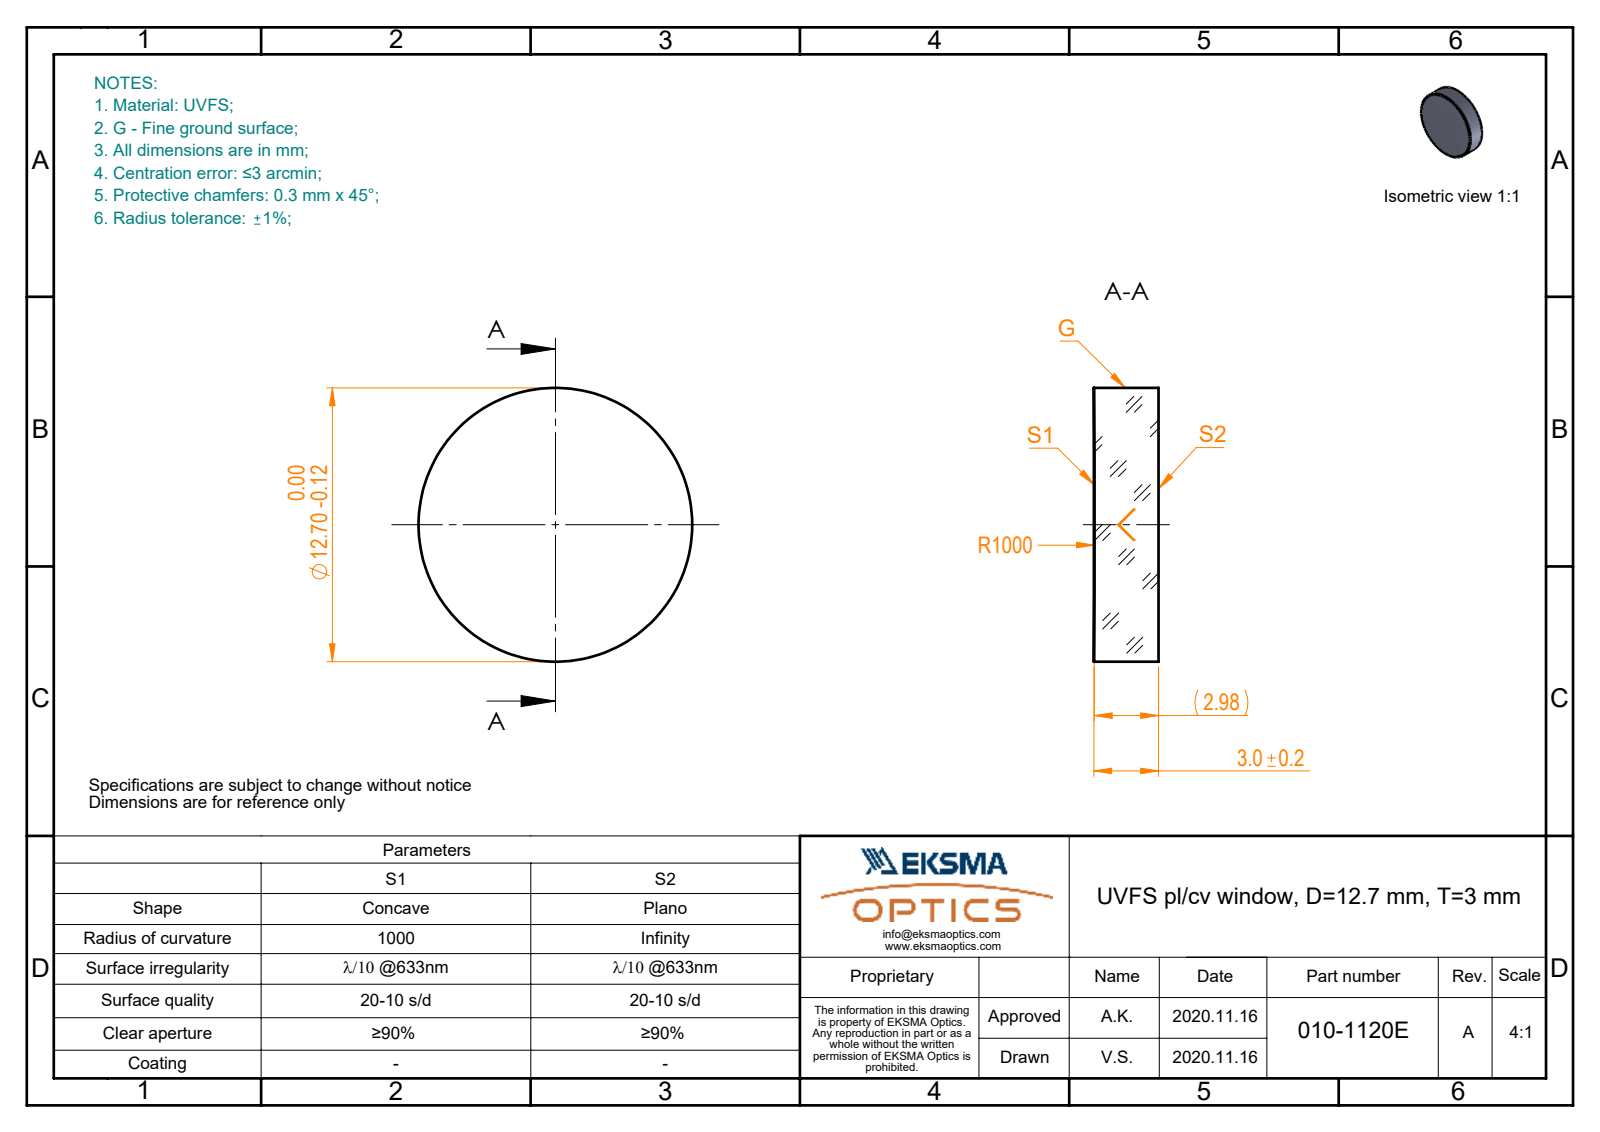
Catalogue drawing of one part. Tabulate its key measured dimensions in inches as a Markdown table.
| quantity | value |
| --- | --- |
| part name | 010-1120E_UVFS_PCV_window |
| STEP written by | SolidWorks 2019 (CONFIG_CONTROL_DESIGN) |
| units | inches |
| bodies | 1 solid, 5 faces (1 planar, 2 cylindrical, 2 other) |
| overall size | 0.5 × 0.5 × 0.118 |
| volume | 0.023 in³ |
| surface area | 0.578 in² |
| round bosses / shafts (diameter × count) | 0.5 × 1 |
